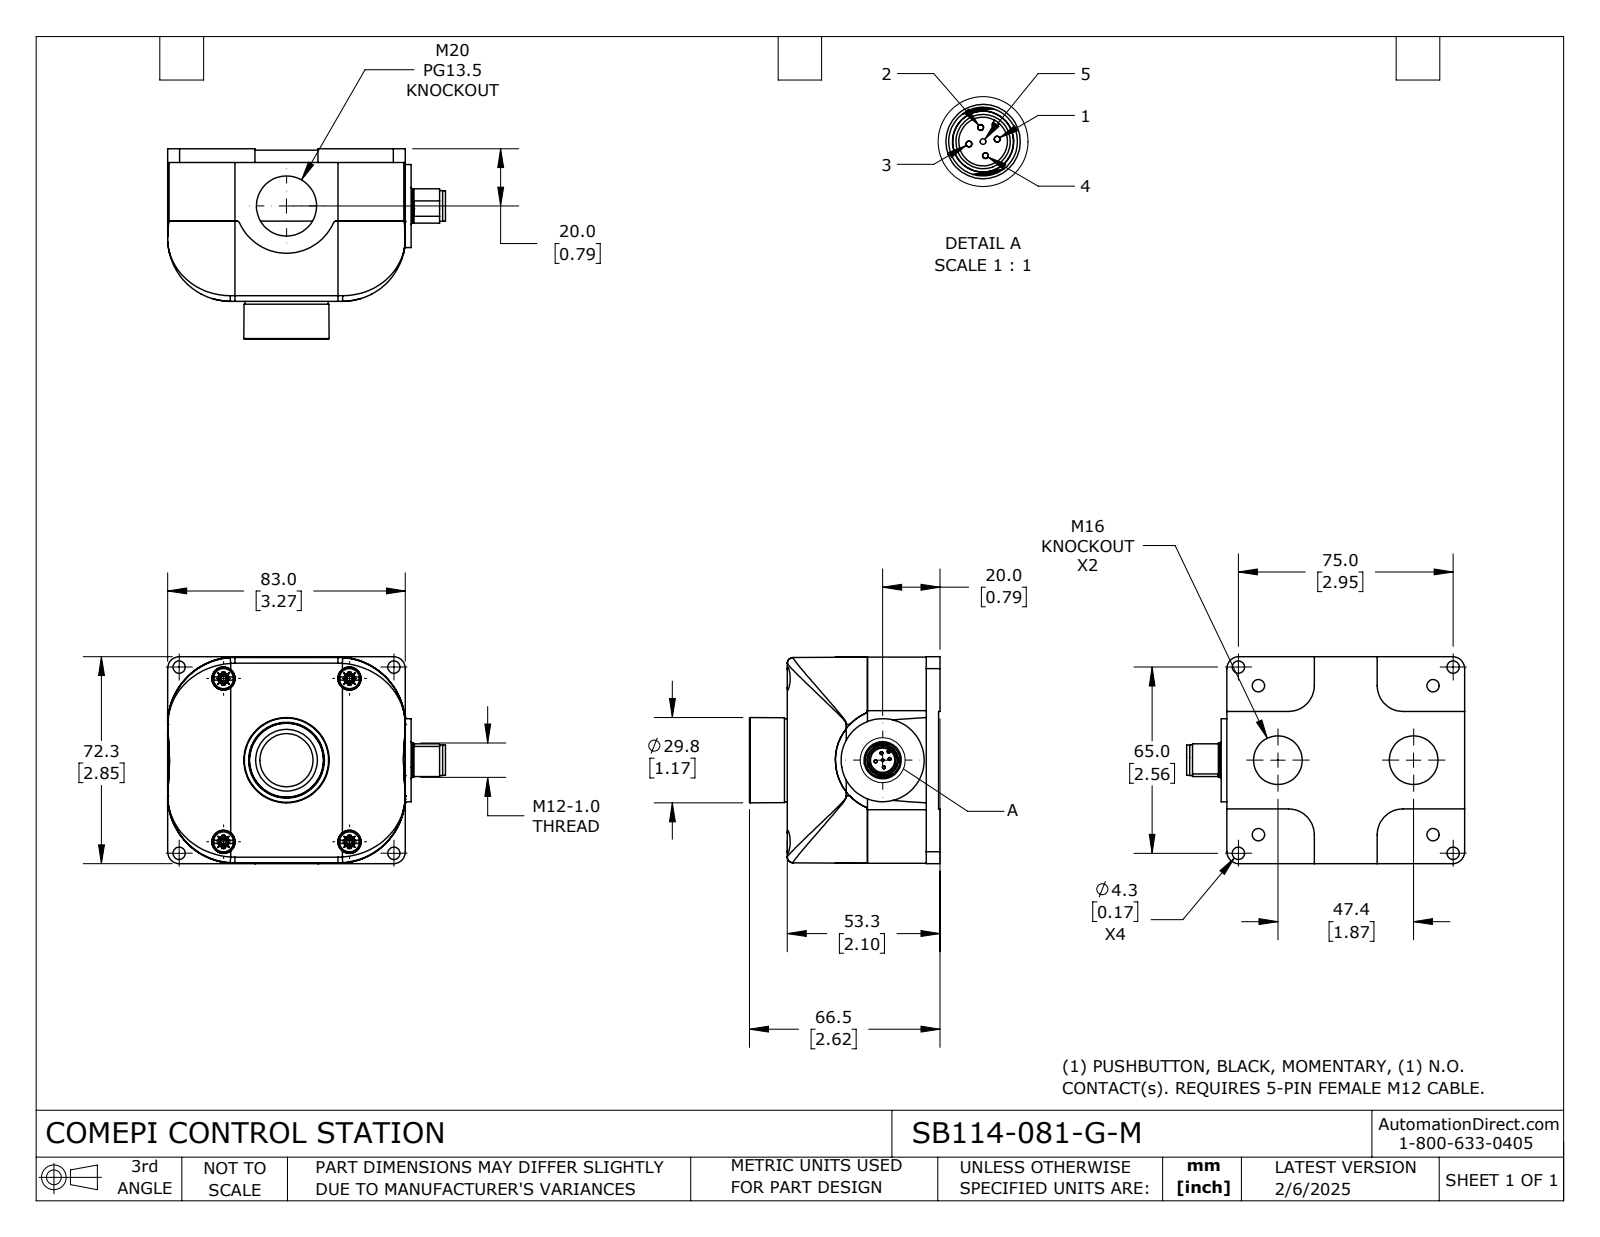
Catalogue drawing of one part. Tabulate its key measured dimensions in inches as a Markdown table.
| quantity | value |
| --- | --- |
| part name | SB114-081-G-M |
| STEP written by | SolidWorks 2024 (CONFIG_CONTROL_DESIGN) |
| units | inches |
| bodies | 10 solids, 786 faces (370 planar, 273 cylindrical, 143 other) |
| overall size | 3.821 × 2.846 × 2.618 |
| volume | 13.23 in³ |
| surface area | 95.33 in² |
| round holes (diameter × count) | 0.169 × 8, 0.04 × 4, 0.067 × 4, 0.087 × 4, 0.323 × 4, 0.669 × 2, 0.827 × 2, 0.335 × 1, 0.531 × 1, 0.713 × 1, 0.854 × 1 |
| round bosses / shafts (diameter × count) | 0.039 × 5, 0.276 × 4, 0.085 × 4, 0.065 × 4, 1.142 × 2, 0.024 × 2, 1.039 × 1, 1.016 × 1 |
| partial cylindrical surfaces (radius × count) | 0.02 × 5, 0.035 × 4, 0.079 × 4, 0.354 × 4, 0.38 × 4, 0.925 × 4, 0.008 × 2, 0.01 × 2 |
| main face-to-face distances | 0.976, 0.098, 0.878, 2.079, 1.98, 1.102, 0.118, 2.098, 0.02, 0.996 |
| hole center spacings | 0.376, 1.058, 1.39, 1.578, 1.954, 2.32, 2.367, 2.689 |
